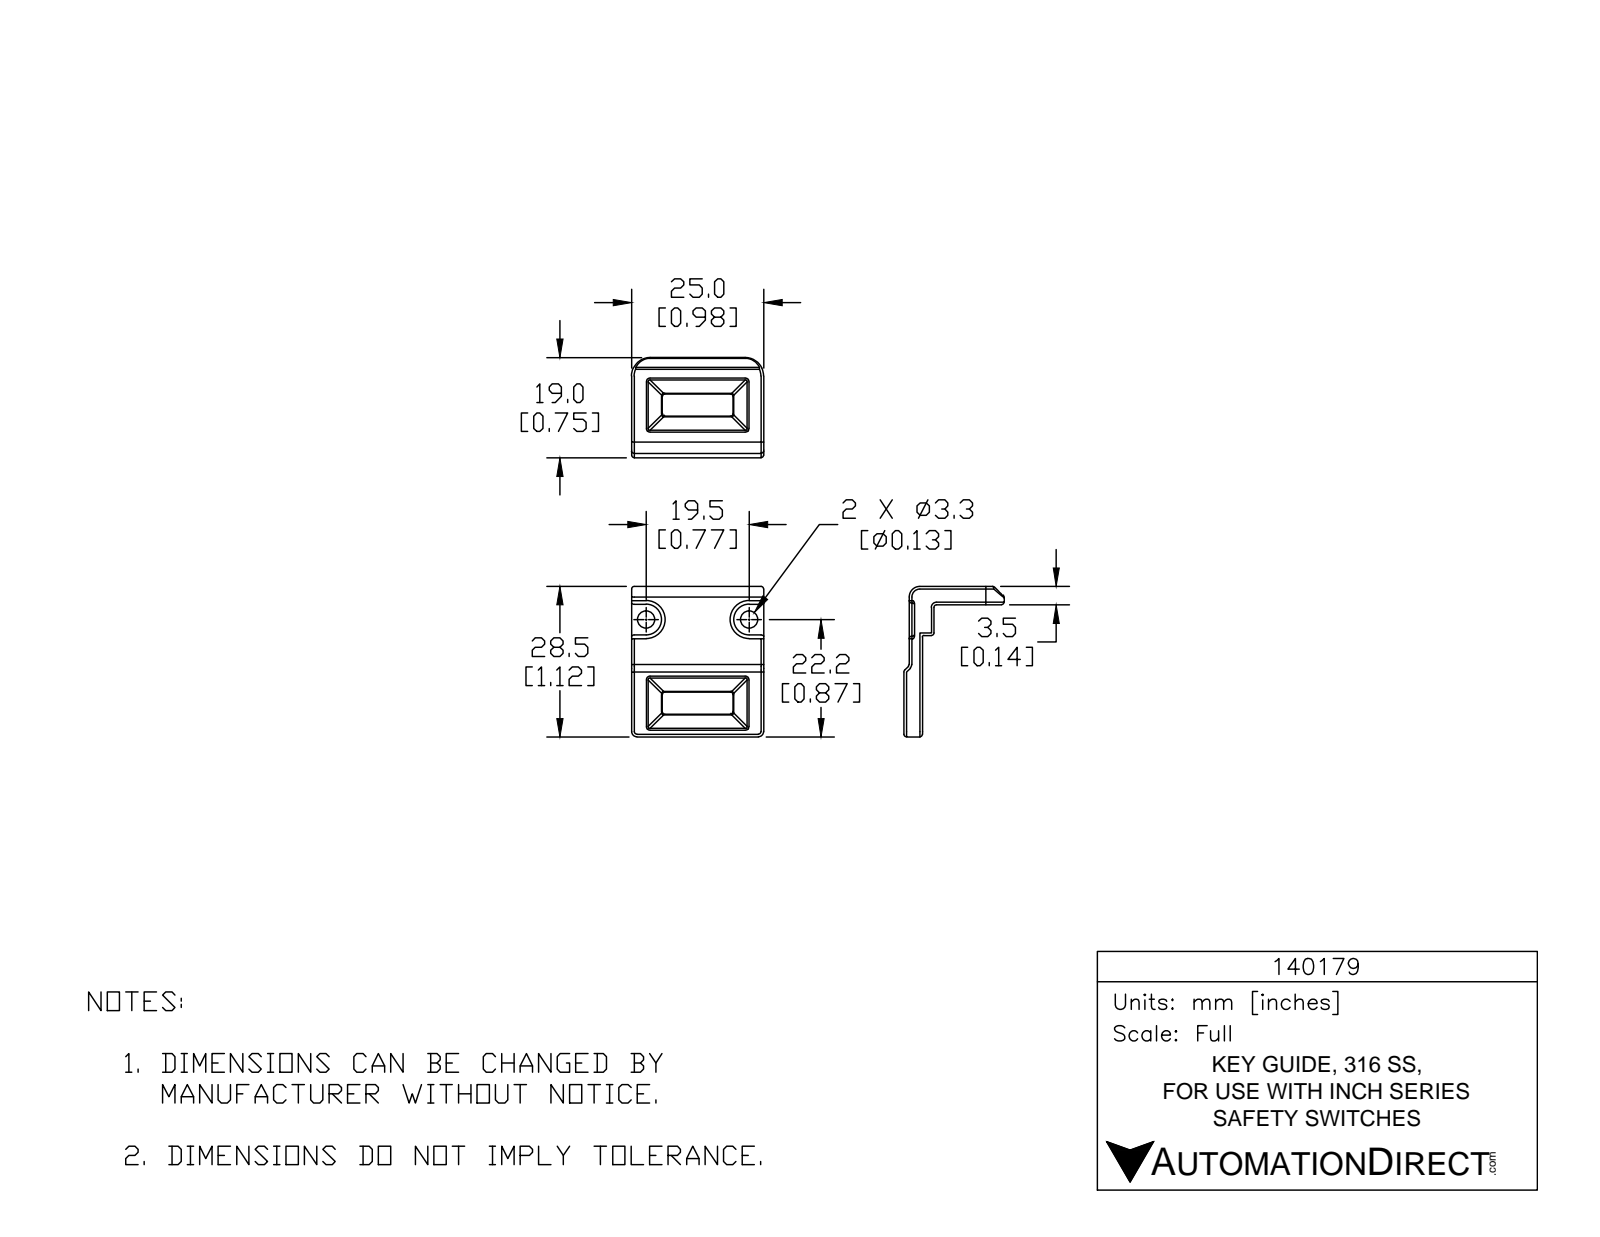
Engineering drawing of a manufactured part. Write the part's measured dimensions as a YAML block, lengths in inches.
part_name: "140179"
step_written_by: "SolidWorks 2014 (AUTOMOTIVE_DESIGN)"
units: inches
bodies: {solids: 1, faces: 216, planar: 39, cylindrical: 96, other: 81}
overall_size: [1.122, 0.984, 0.748]
volume: 0.161
surface_area: 3.906
round_holes:
  - {diameter: 0.13, count: 2}
partial_cylinders:
  - {radius: 0.02, count: 67}
  - {radius: 0.012, count: 4}
  - {radius: 0.008, count: 2}
  - {radius: 0.039, count: 2}
  - {radius: 0.118, count: 2}
  - {radius: 0.122, count: 2}
  - {radius: 0.138, count: 2}
  - {radius: 0.079, count: 1}
face_to_face_distances: [0.098, 0.138, 0.984, 0.039, 1.122, 0.337, 0.621, 0.952, 0.331, 0.059]
hole_center_spacings: [0.768]
